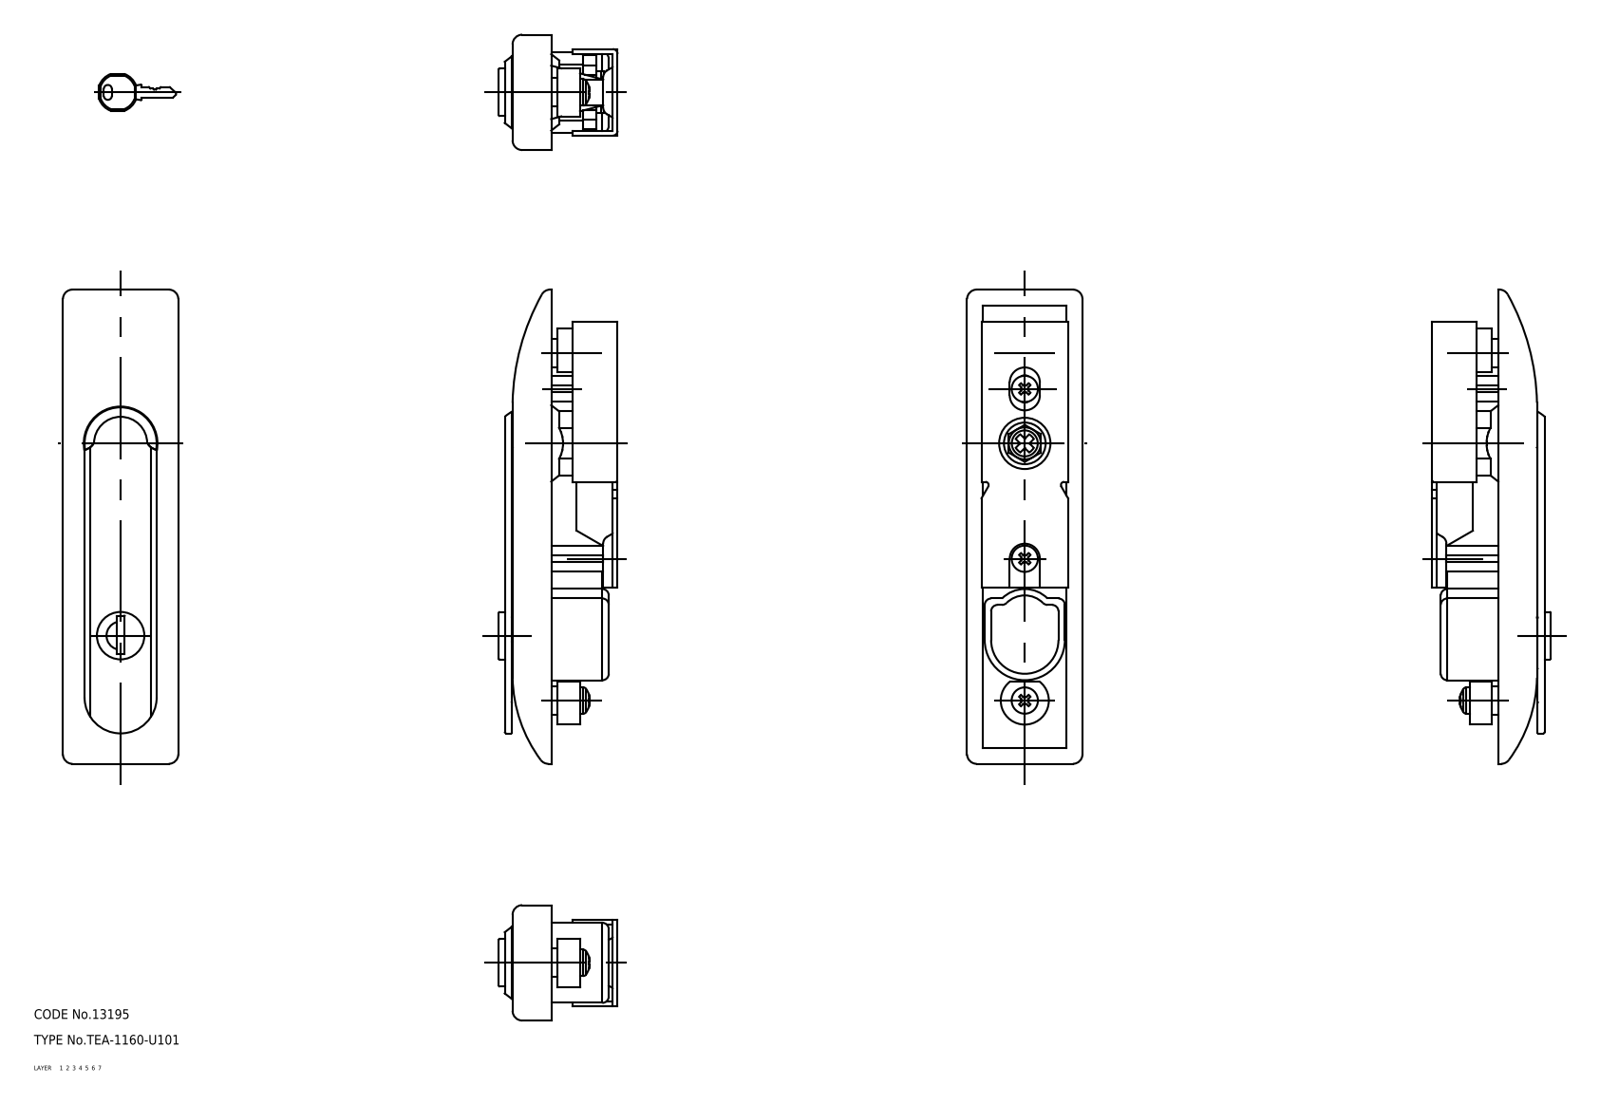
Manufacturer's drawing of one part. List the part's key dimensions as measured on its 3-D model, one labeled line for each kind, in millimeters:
Part name (STEP PRODUCT): screw; spacer; key; cover (+3 more)
STEP written by: CADfix (AUTOMOTIVE_DESIGN)
Units: millimetres
Bodies: 8 solids, 479 faces (0 planar, 0 cylindrical, 479 other)
Overall size (bounding box): 148 × 101.46 × 36
Volume: 69 385 mm³ · Surface area: 45 497 mm²
